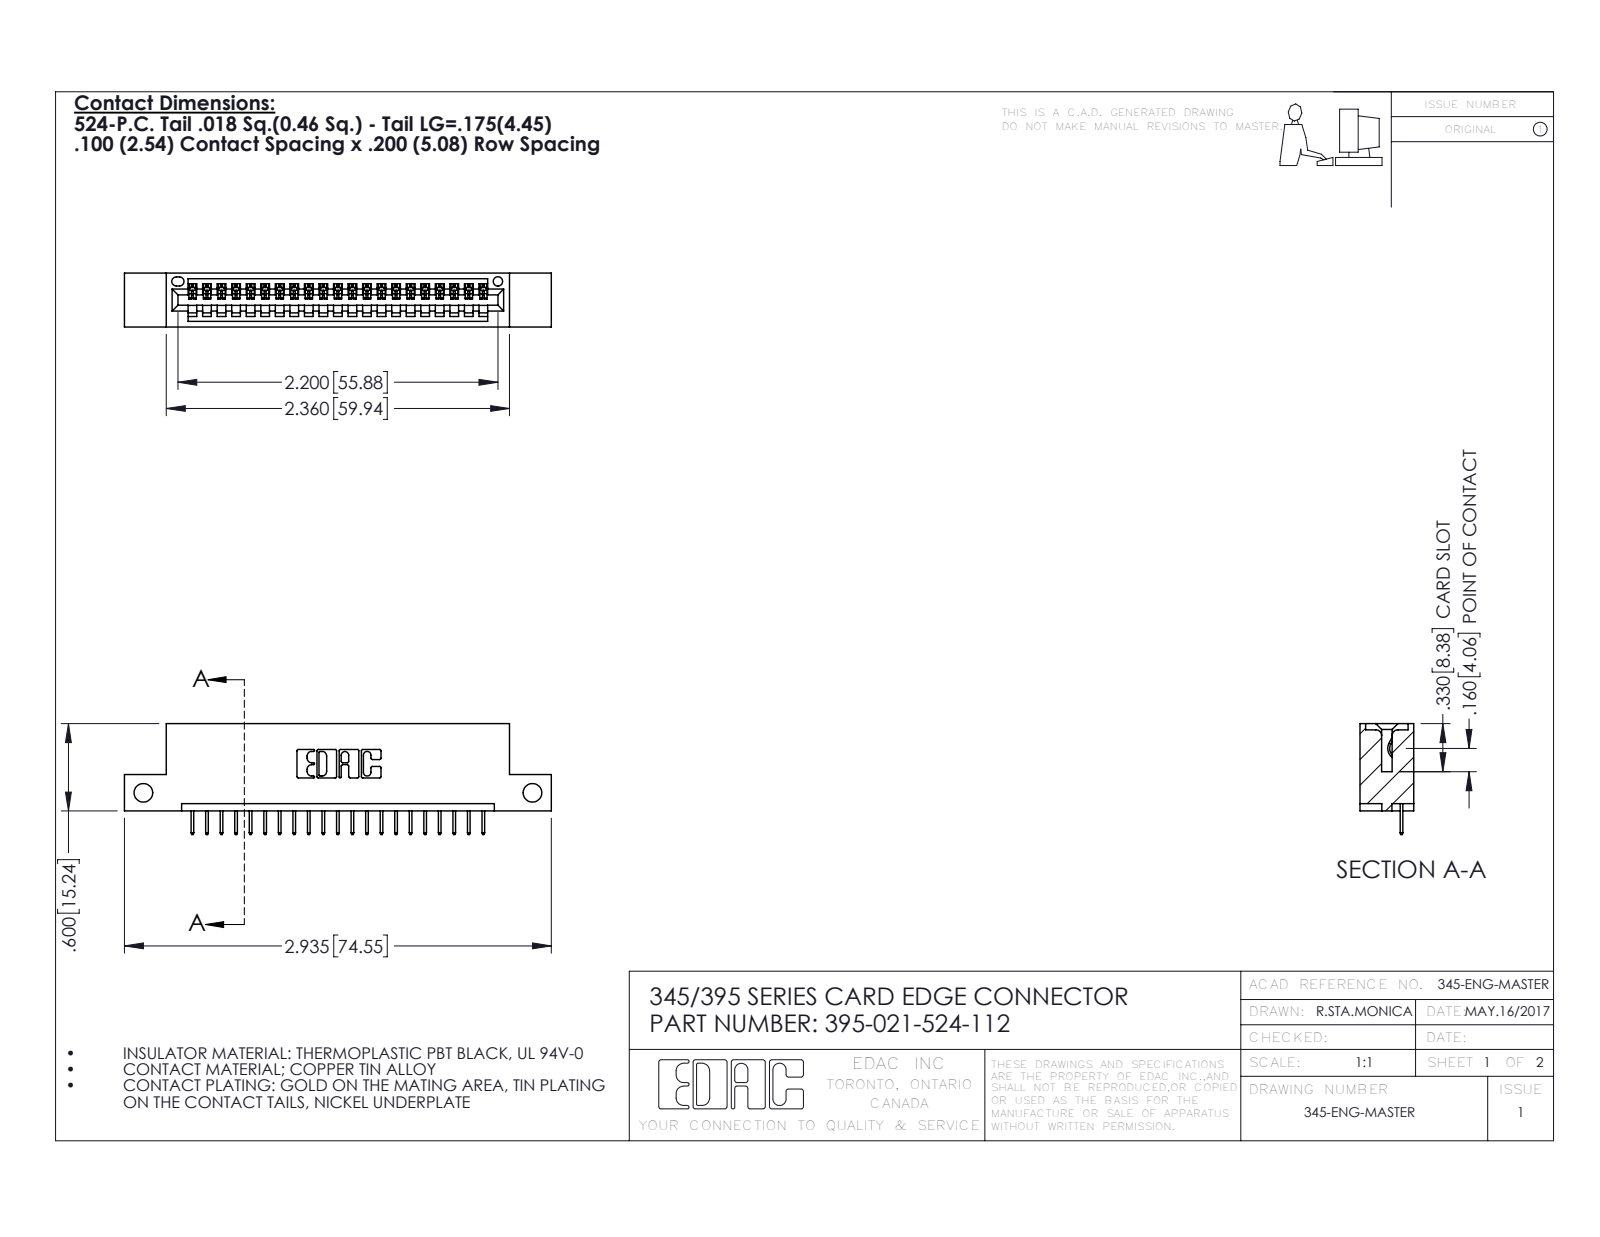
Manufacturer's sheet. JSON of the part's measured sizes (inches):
{"part_name": "395-021-524-112; 345 Part_Flush Mounting Lugs - Side Mount; 345-292-001_345-293-124", "step_written_by": "SolidWorks 2016 (CONFIG_CONTROL_DESIGN)", "units": "inches", "bodies": {"solids": 22, "faces": 1428, "planar": 1046, "cylindrical": 382, "other": 0}, "overall_size": [2.935, 0.762, 0.37], "volume_in3": 0.411, "surface_area_in2": 12.81, "round_holes": [[0.128, 2], [0.064, 1]], "partial_cylinders_radius": [[0.006, 42], [0.01, 22], [0.007, 6], [0.031, 6], [0.026, 3], [0.031, 2], [0.04, 2], [0.014, 1]], "face_to_face_distances": [0.298, 0.072, 0.2, 0.37, 0.098, 0.272, 0.025, 0.225, 0.072, 0.149], "hole_center_spacings": [2.675]}
